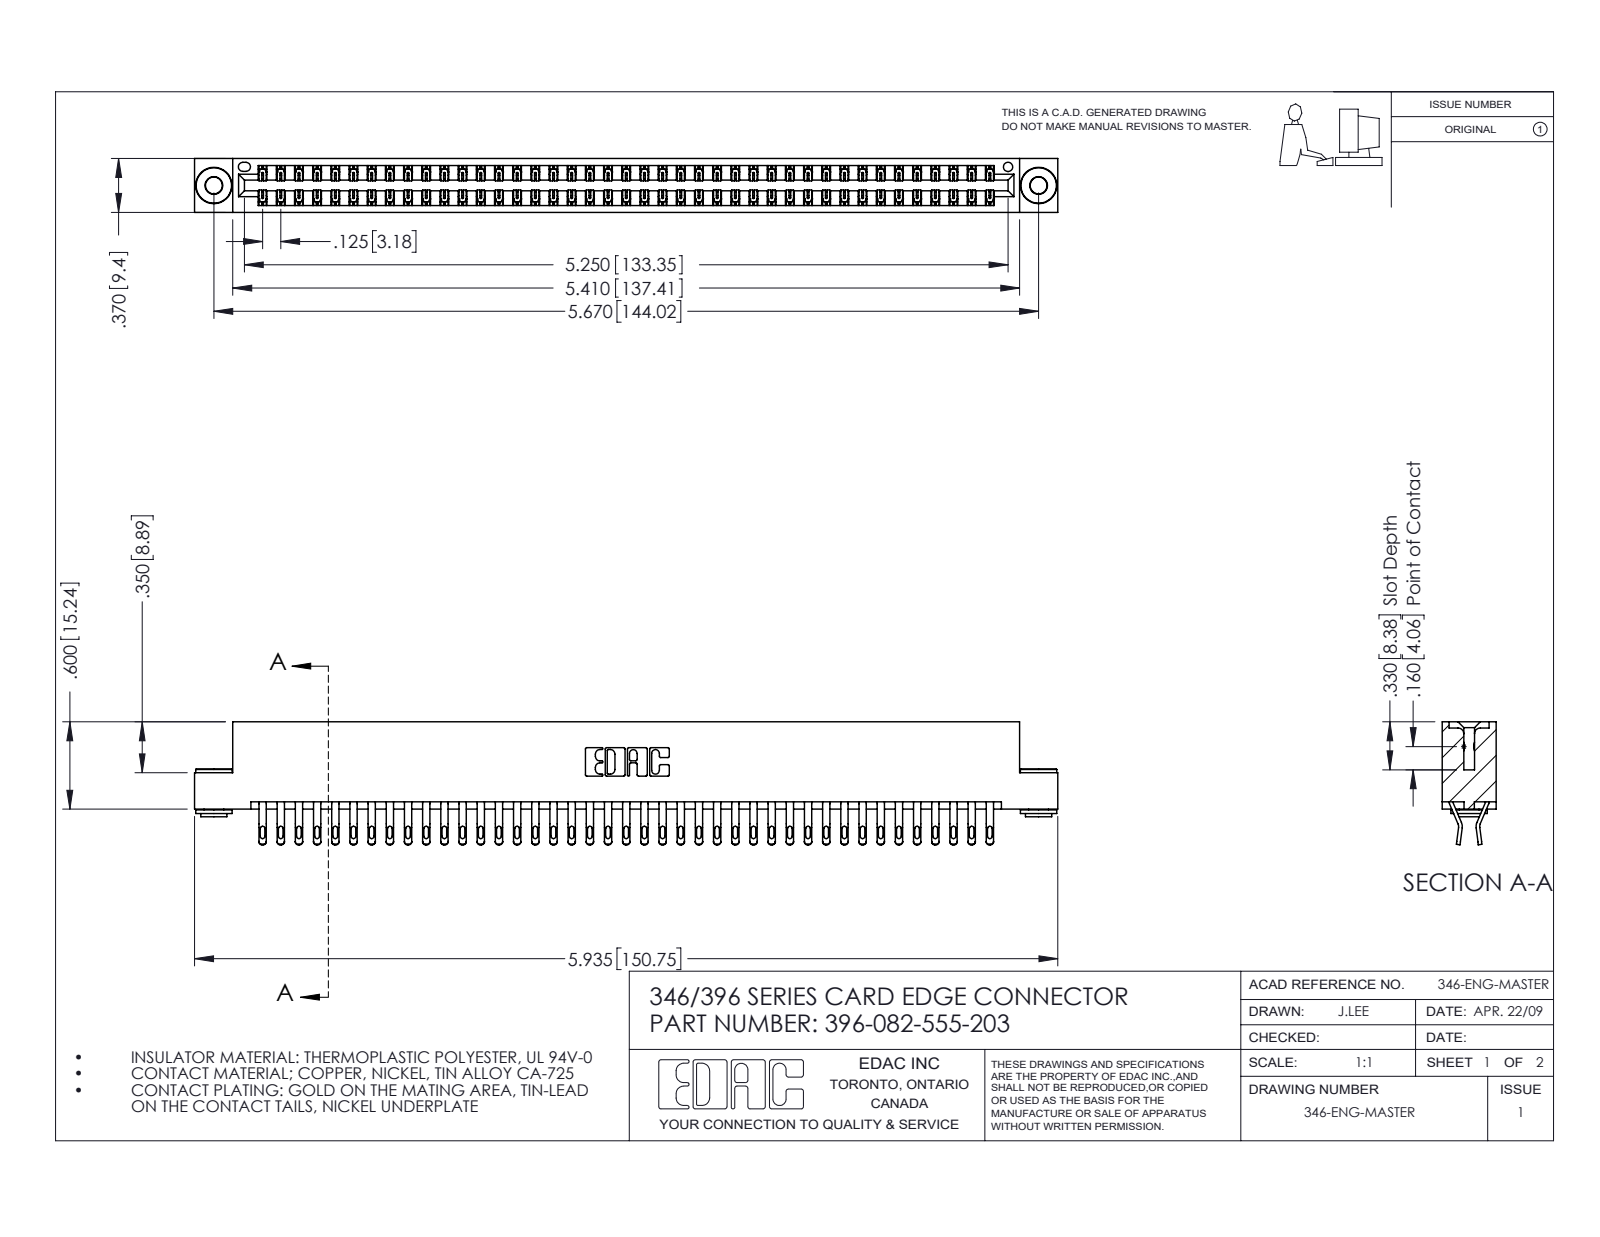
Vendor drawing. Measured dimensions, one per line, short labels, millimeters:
name: 396-082-555-203; 346 Part_Flush Mounting Lugs - 0.156 Dia-TH; 345-250-002_345-250-002-102; 345-292-001_555 Tail
written by: SolidWorks 2016 (CONFIG_CONTROL_DESIGN)
unit: mm
bodies: 85 solids, 4916 faces (2792 planar, 2116 cylindrical, 8 other)
size: 150.7 × 21.5 × 9.4
volume: 14 900 mm³; area: 21 590 mm²
holes: 2× ⌀2.9, 2× ⌀4, 1× ⌀1.6
bosses: 2× ⌀6.4, 2× ⌀4.6, 2× ⌀3.5
rounds: 164× R0.4, 164× R0.5, 123× R0.2, 22× R0.3, 6× R0.2, 6× R0.8, 3× R0.7, 2× R0.3
face distances: 1.2, 8.2, 9.4, 6.4, 0.6, 1.8, 7.6, 7, 3.8, 5.6
hole spacings: 6.2, 138.7, 144
